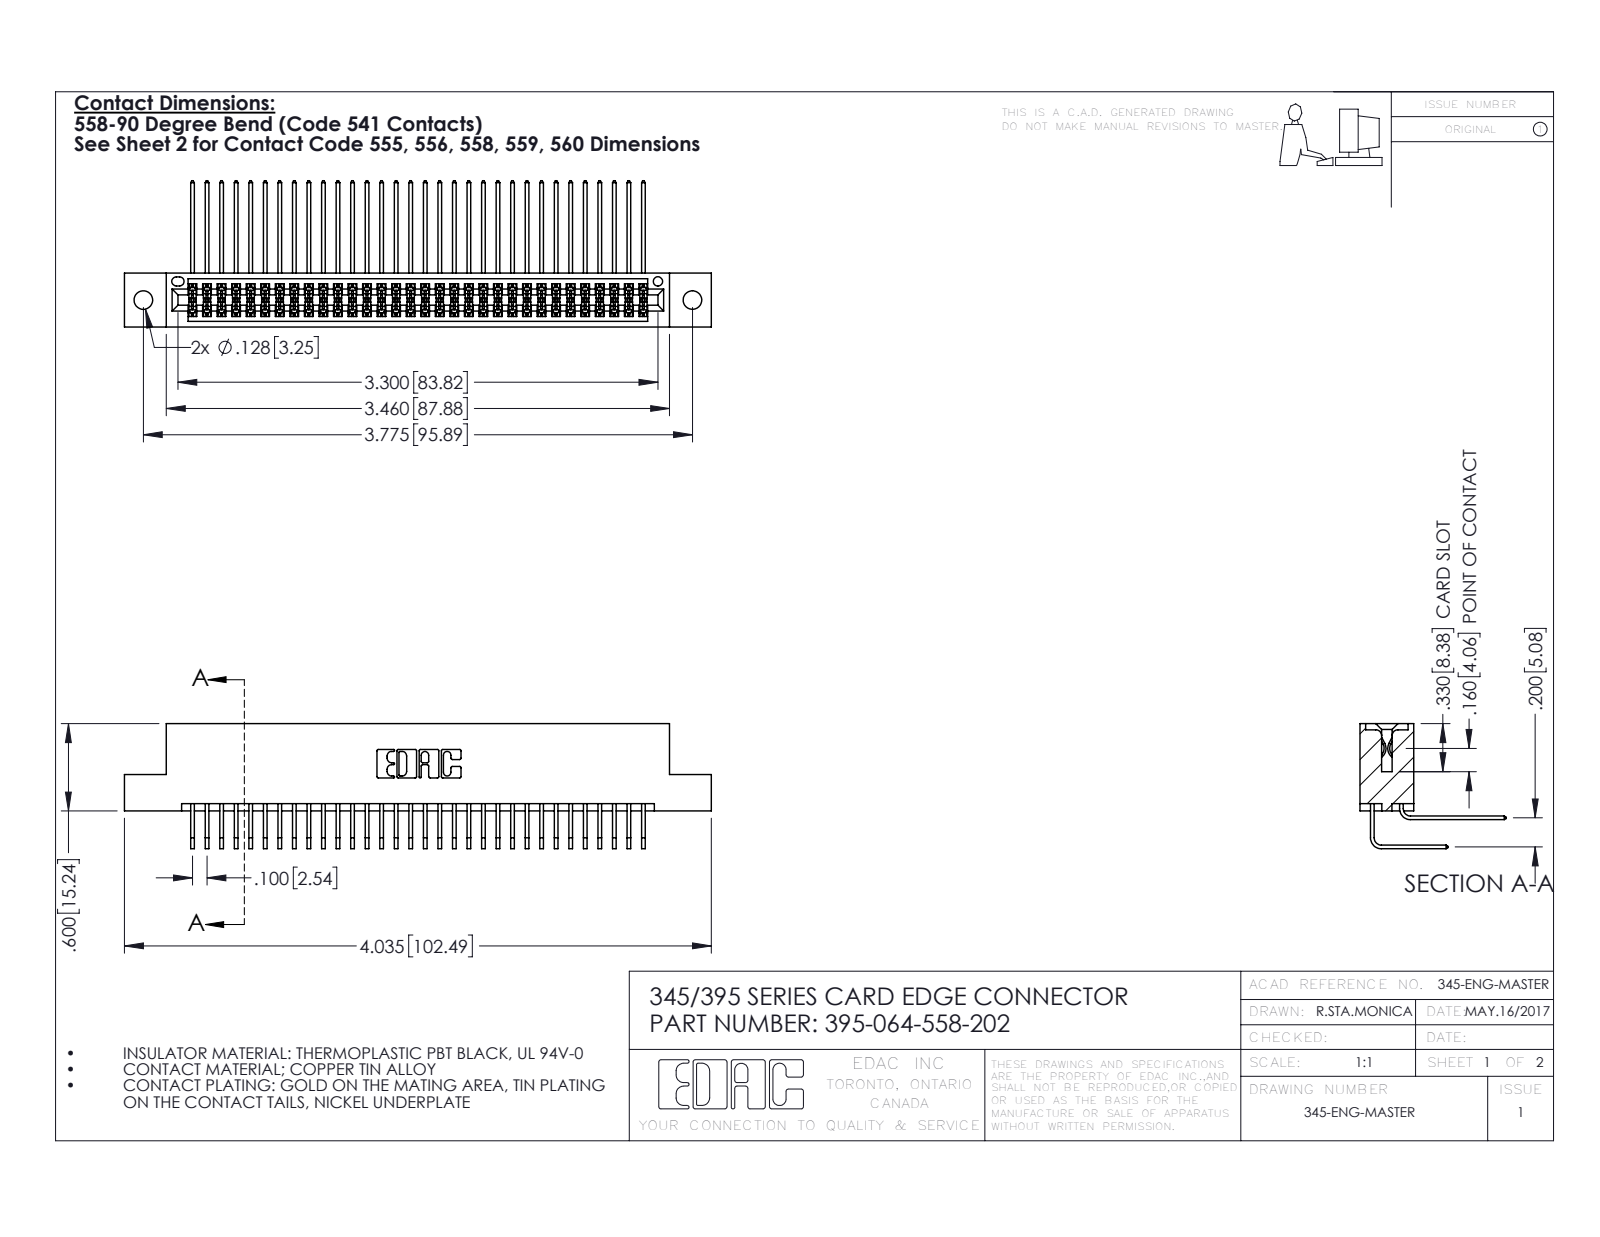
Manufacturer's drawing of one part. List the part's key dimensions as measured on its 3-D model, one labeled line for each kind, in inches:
Part name (STEP PRODUCT): 345 Part_Flush Mounting Lugs - 0.128 Dia; 395-064-558-202; 345-292-001_558 Tail - 2; 345-292-001_558 559 Tail - 1
STEP written by: SolidWorks 2016 (CONFIG_CONTROL_DESIGN)
Units: inches
Bodies: 65 solids, 3454 faces (2320 planar, 1134 cylindrical, 0 other)
Overall size (bounding box): 4.035 × 1.005 × 0.859
Volume: 0.622 in³ · Surface area: 25.33 in²
Round holes (diameter × count): ⌀0.128 ×2, ⌀0.064 ×1
Partial cylindrical surfaces — rounded edges, fillets, slot ends (radius × count): R0.006 ×97, R0.01 ×22, R0.007 ×6, R0.031 ×6, R0.026 ×3, R0.014 ×2, R0.019 ×2, R0.022 ×2
Main face-to-face distances: 0.2, 0.072, 0.298, 0.37, 0.098, 0.272, 0.025, 0.225, 0.025, 0.285
Hole centre spacings: 0.27, 3.54, 3.775
